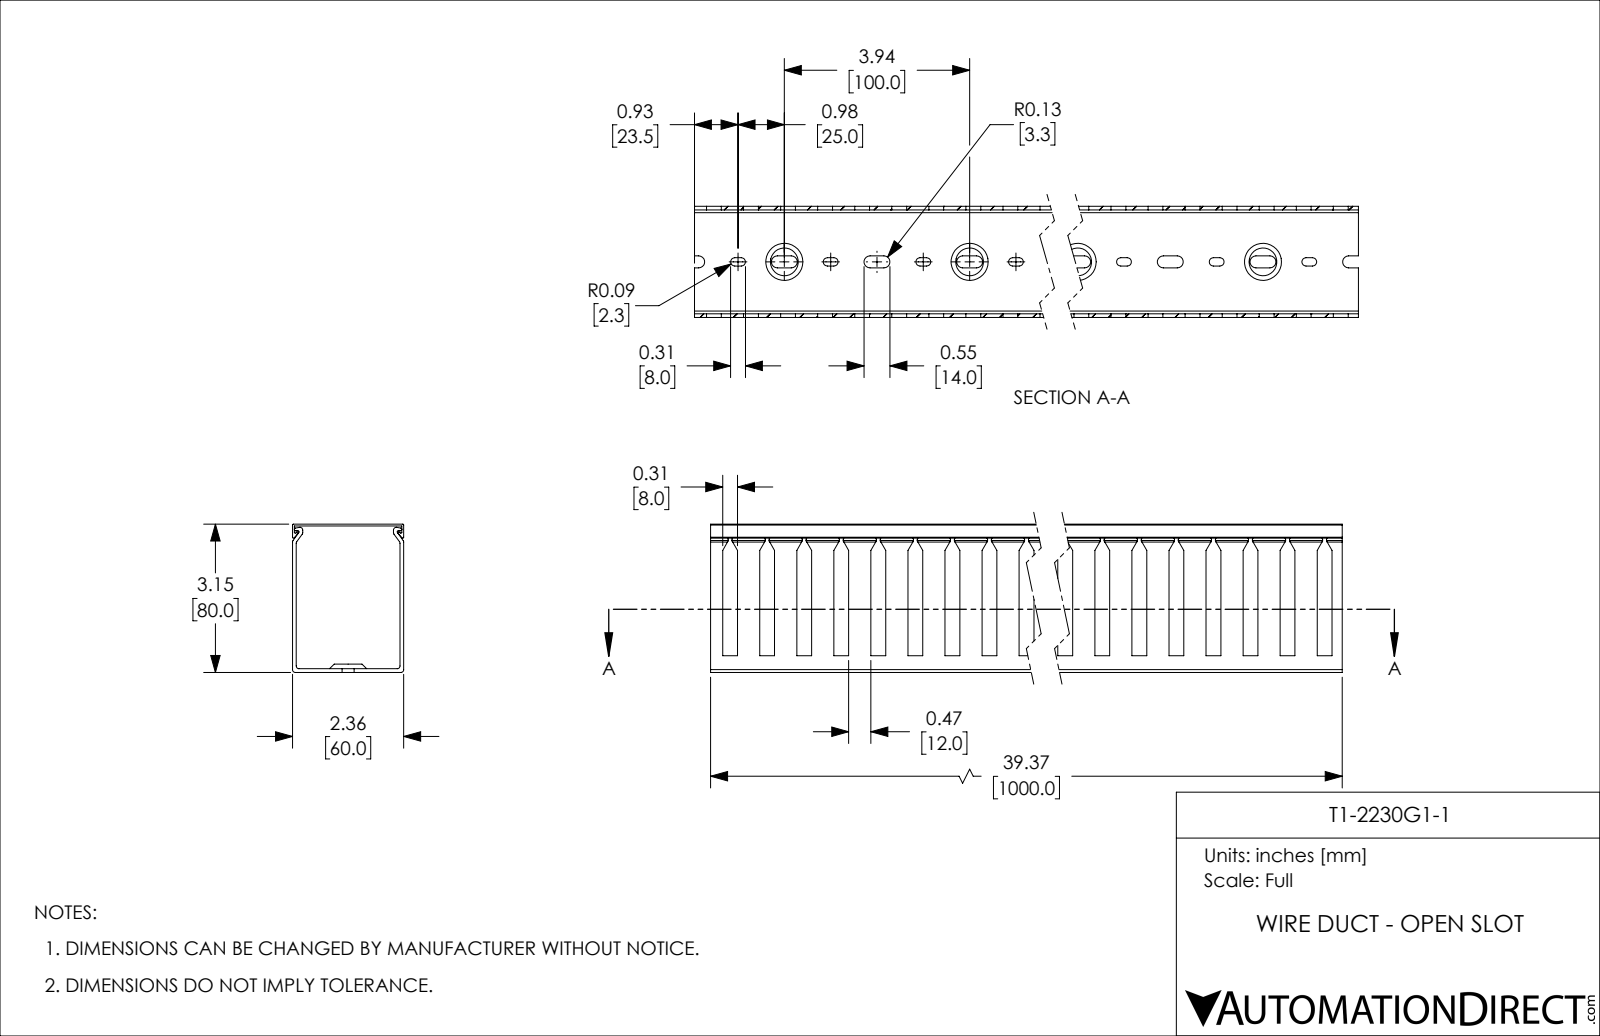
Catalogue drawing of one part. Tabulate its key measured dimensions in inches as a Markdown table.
| quantity | value |
| --- | --- |
| part name | T1-2230G1-1 |
| STEP written by | SolidWorks 2021 (CONFIG_CONTROL_DESIGN) |
| units | inches |
| bodies | 2 solids, 775 faces (444 planar, 311 cylindrical, 20 other) |
| overall size | 39.37 × 3.15 × 2.362 |
| volume | 30.11 in³ |
| surface area | 893.2 in² |
| partial cylindrical surfaces (radius × count) | 0.089 × 40, 0.128 × 40, 0.059 × 12, 0.02 × 8, 0.03 × 6 |
| main face-to-face distances | 0.079, 2.283, 2.362, 0.039, 2.205, 3.15, 3.11, 3.031, 3.071, 2.323 |
